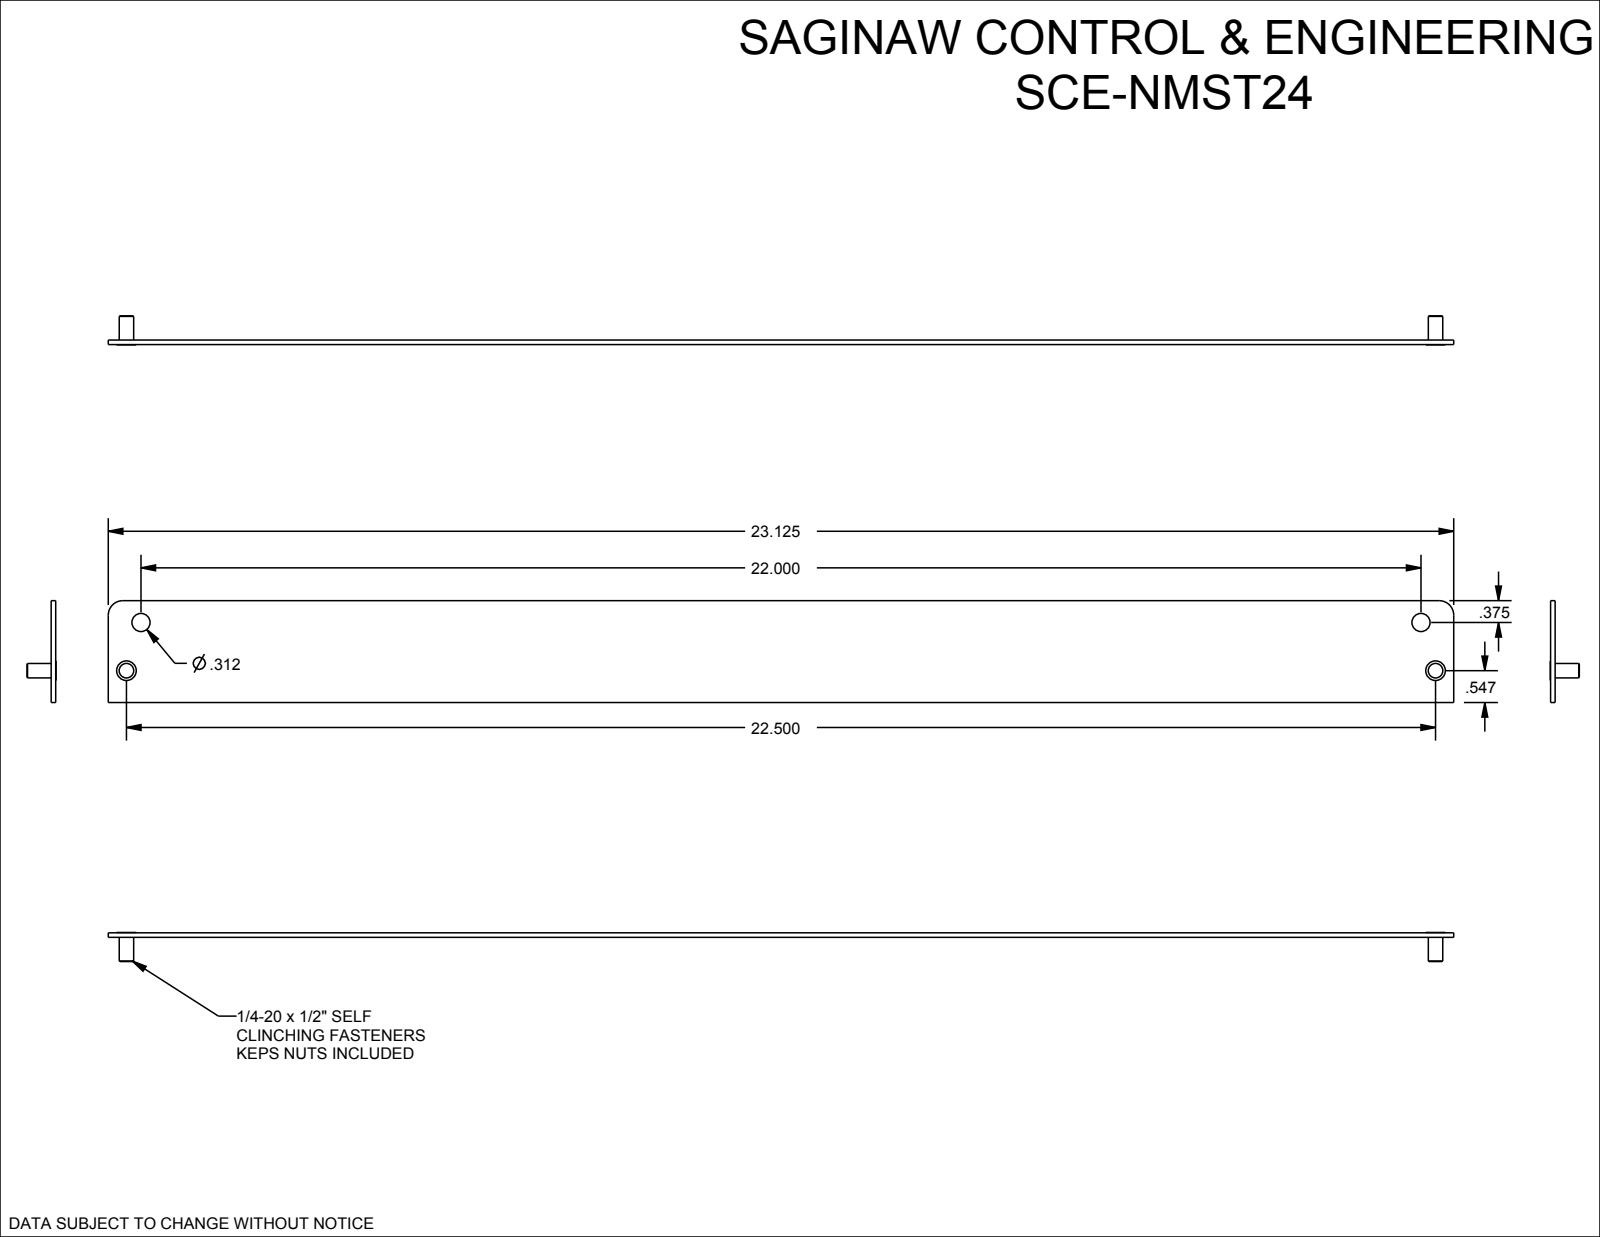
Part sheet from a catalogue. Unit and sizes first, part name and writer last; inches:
Units: inches
Overall size (bounding box): 23.125 × 1.75 × 0.5
Round holes (diameter × count): ⌀0.25 ×2, ⌀0.312 ×2
Round bosses / shafts (diameter × count): ⌀0.337 ×2, ⌀0.248 ×2
Partial cylindrical surfaces — rounded edges, fillets, slot ends (radius × count): R0.25 ×2
Main face-to-face distances: 0.078, 1.75, 0.084, 23.125, 0.066, 0.018, 0.416, 0.482, 0.494, 0.5
Hole centre spacings: 0.865, 22.265, 22, 22.5
Volume: 3.185 in³ · Surface area: 85.66 in²
Bodies: 3 solids, 24 faces (12 planar, 10 cylindrical, 2 other)
Part name (STEP PRODUCT): SCE-NMST24
STEP written by: SolidWorks 2019 (AUTOMOTIVE_DESIGN)
